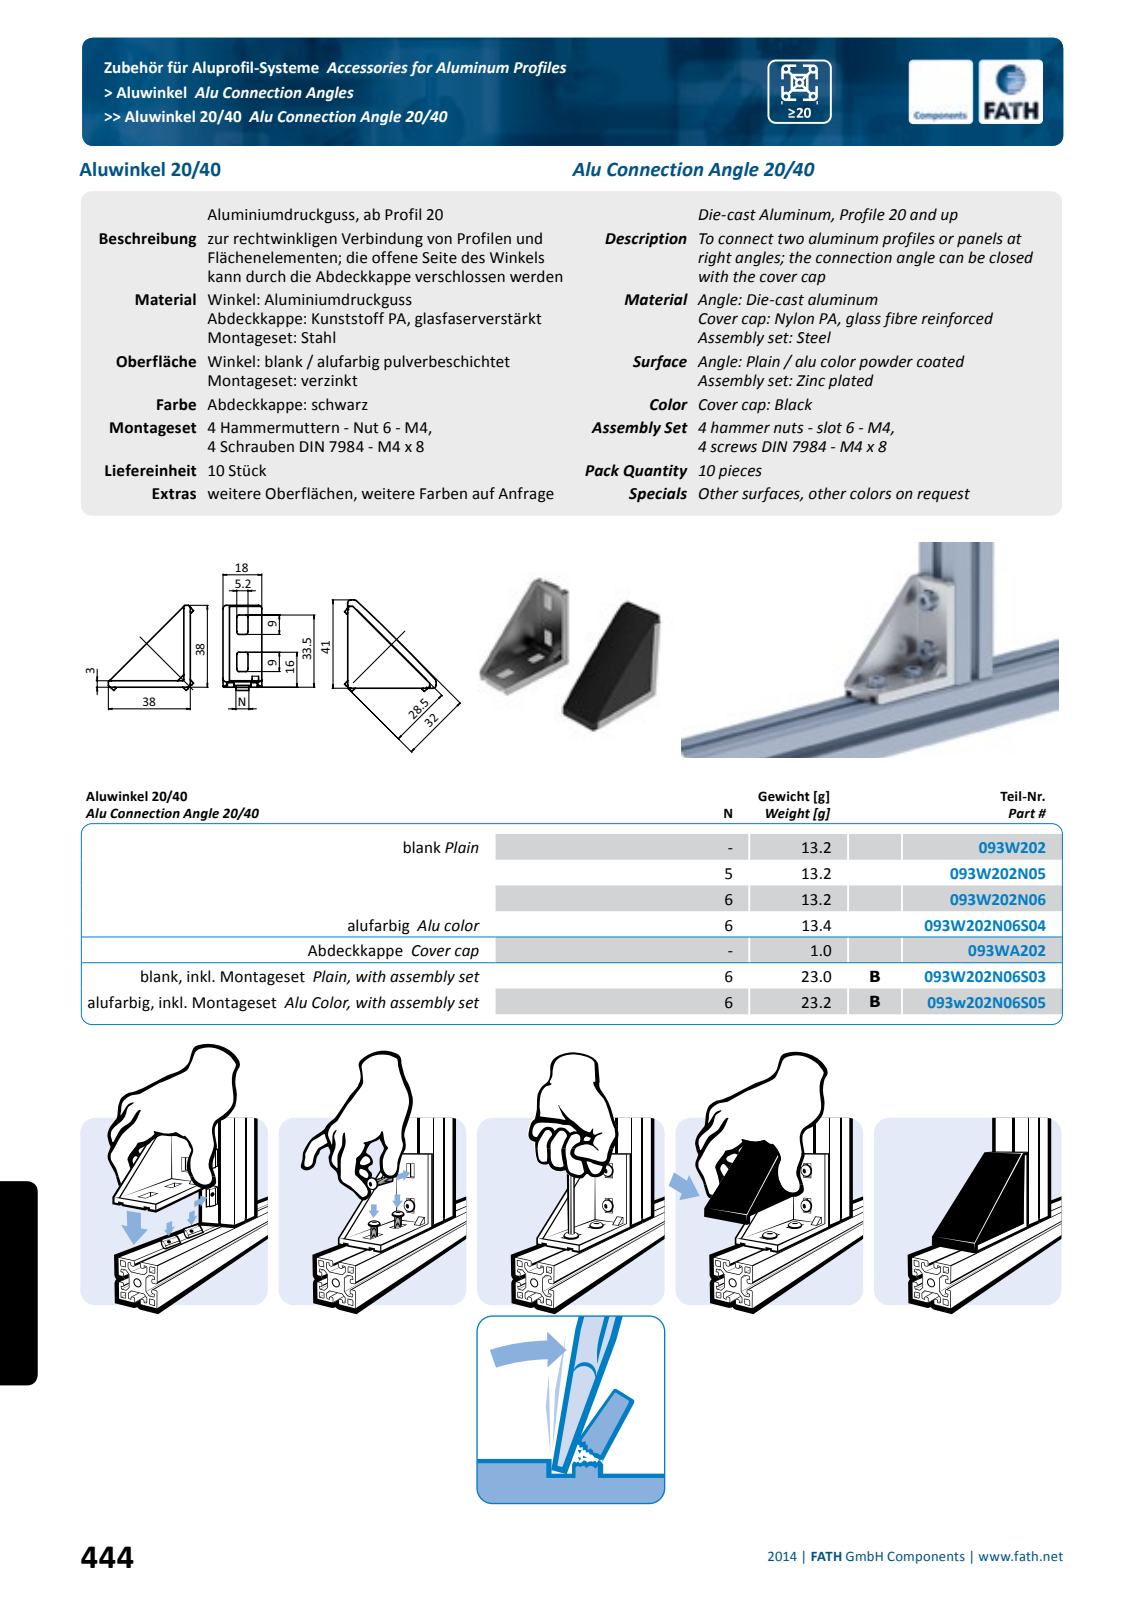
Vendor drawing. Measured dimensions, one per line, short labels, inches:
name: fath_093w202n05
written by: Spatial InterOp 3D (automotive_design)
unit: in
bodies: 1 solid, 169 faces (82 planar, 54 cylindrical, 33 other)
size: 1.555 × 1.555 × 0.709
volume: 0.3 in³; area: 6.611 in²
rounds: 20× R0.012, 17× R0.039, 5× R0.02, 4× R0.059
face distances: 0.118, 1.496, 1.378, 1.024, 0.093, 0.326, 1.522, 0.11, 0.436, 1.633
